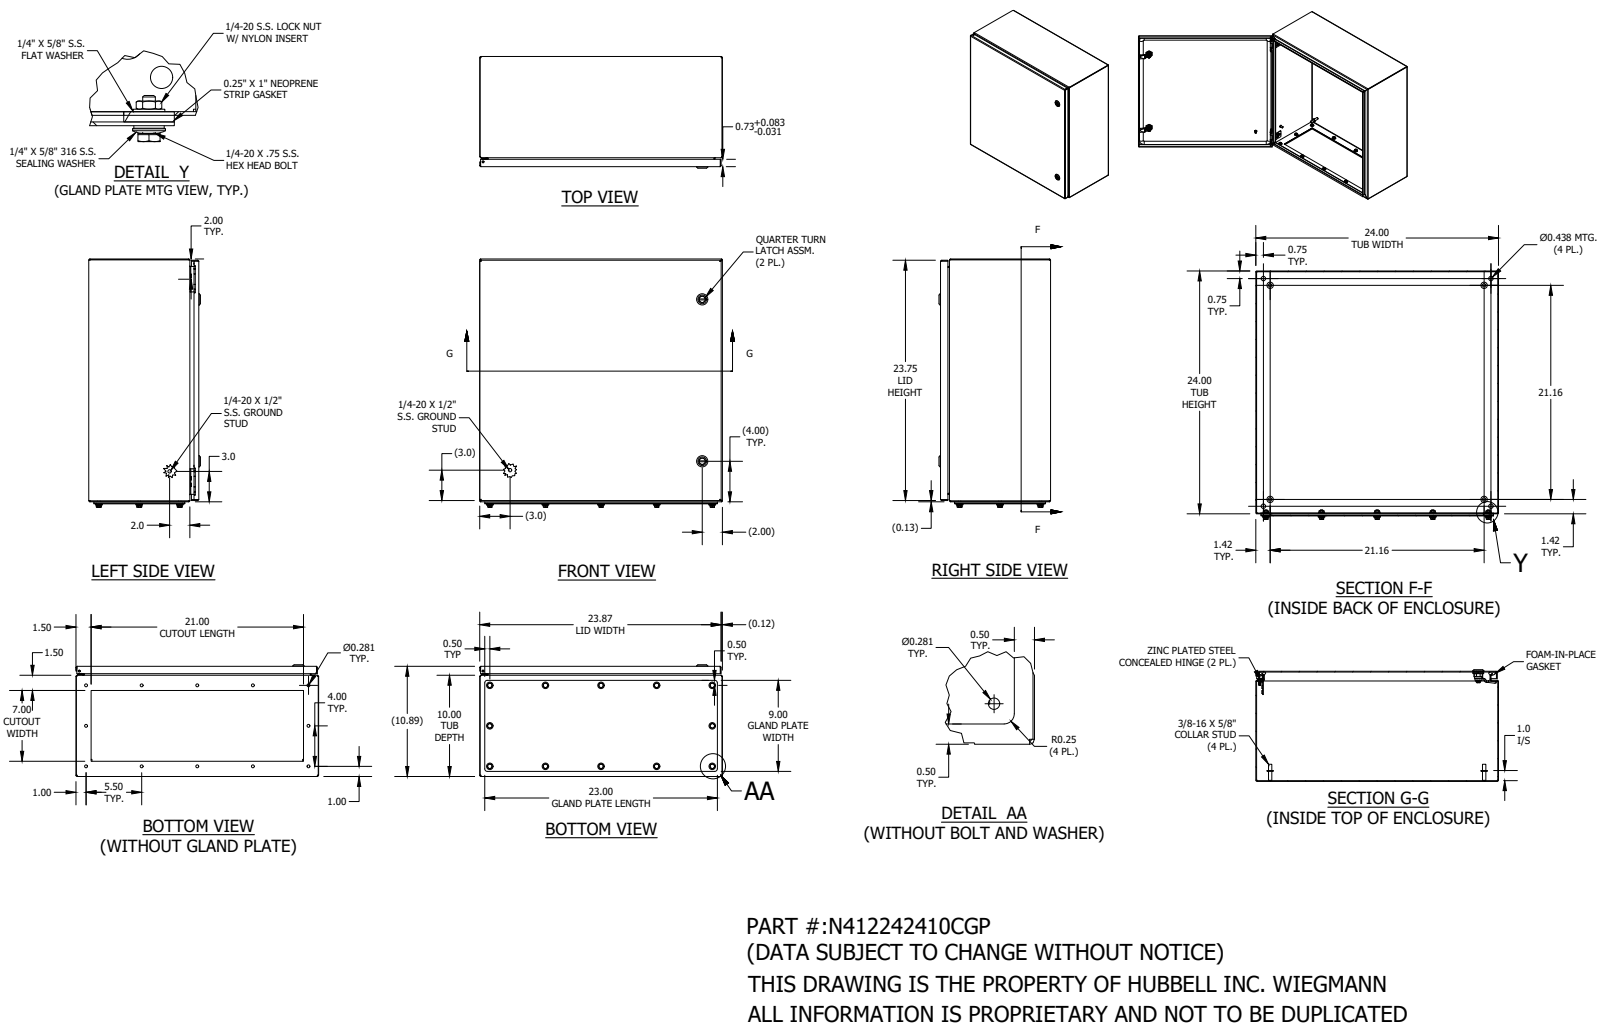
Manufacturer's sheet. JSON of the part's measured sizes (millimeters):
{"part_name": "N412242410CGP", "step_written_by": "SolidWorks 2019 (AUTOMOTIVE_DESIGN)", "units": "millimeters", "bodies": {"solids": 95, "faces": 2687, "planar": 1101, "cylindrical": 810, "other": 776}, "overall_size": [622.8, 609.6, 280.5], "volume_mm3": 3353000, "surface_area_mm2": 3295000, "round_holes": [[7.1, 14], [5.4, 12], [7.4, 12], [7, 9], [4.1, 8], [6, 6], [6, 6], [8.9, 6], [4.8, 5], [2.4, 4], [4.2, 4], [11.1, 4]], "round_bosses_or_shafts": [[6.4, 22], [15.9, 14], [16.5, 12], [15.2, 12], [11.1, 12], [9.1, 4], [8.4, 4], [8.1, 4]], "partial_cylinders_radius": [[0.3, 56], [1.3, 26], [0.5, 21], [1.2, 20], [3.1, 20], [4, 9], [3.2, 8], [3.3, 8]], "face_to_face_distances": [1.9, 274.6, 272.7, 276.5, 1.9, 607.7, 612.9, 605.8, 611, 609.6], "hole_center_spacings": [101.6, 139.7, 203.2, 279.4, 568, 172.7, 419.1, 431.2]}
